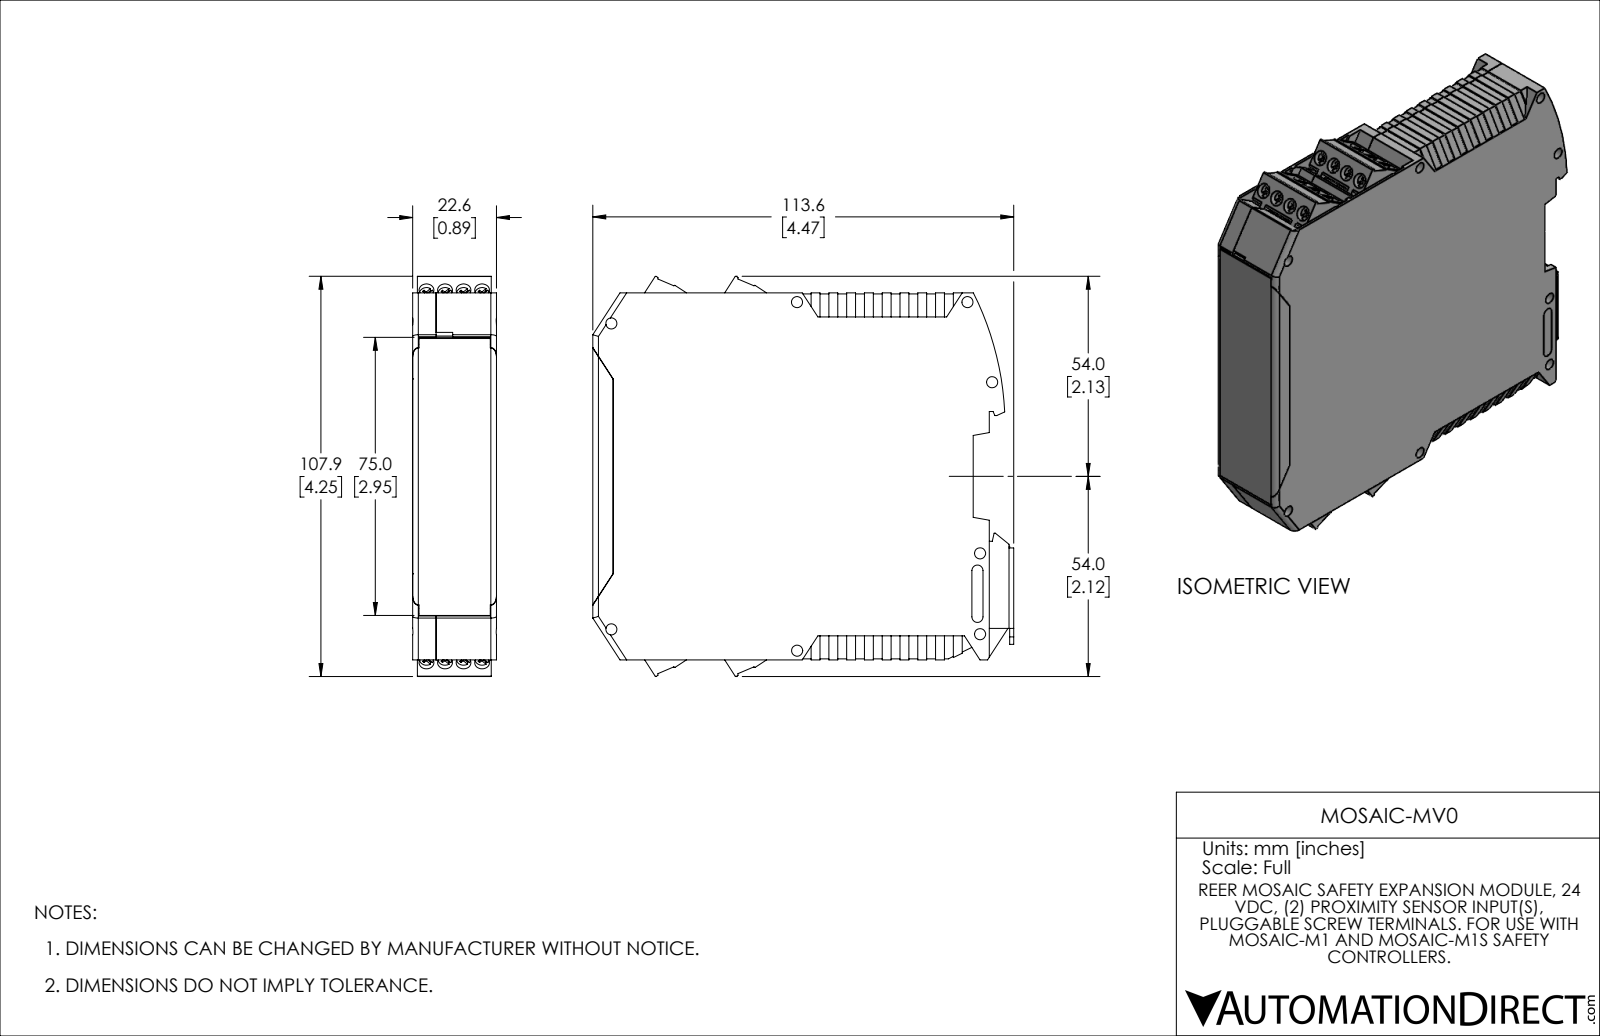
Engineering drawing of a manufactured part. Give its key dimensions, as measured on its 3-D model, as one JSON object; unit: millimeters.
{"part_name": "MOSAIC-MV0", "step_written_by": "SolidWorks 2021 (AUTOMOTIVE_DESIGN)", "units": "millimeters", "bodies": {"solids": 9, "faces": 1954, "planar": 1569, "cylindrical": 379, "other": 6}, "overall_size": [113.6, 108, 22.6], "volume_mm3": 57090, "surface_area_mm2": 75810, "round_holes": [[1.4, 18], [2.8, 16], [4, 16], [3, 14], [1.6, 1]], "round_bosses_or_shafts": [[3.8, 16], [4.5, 1], [2.8, 1], [1.3, 1]], "partial_cylinders_radius": [[0.3, 33], [2.9, 16], [0.2, 12], [0.8, 12], [1.5, 8], [0.8, 6], [2.5, 5], [0.6, 4]], "face_to_face_distances": [1.2, 21.4, 22.6, 20.1, 1, 6.3, 1.2, 5.1, 15.1, 16.3], "hole_center_spacings": [5, 10, 15, 12.8, 12.8, 18.8, 18.8, 11.8]}
